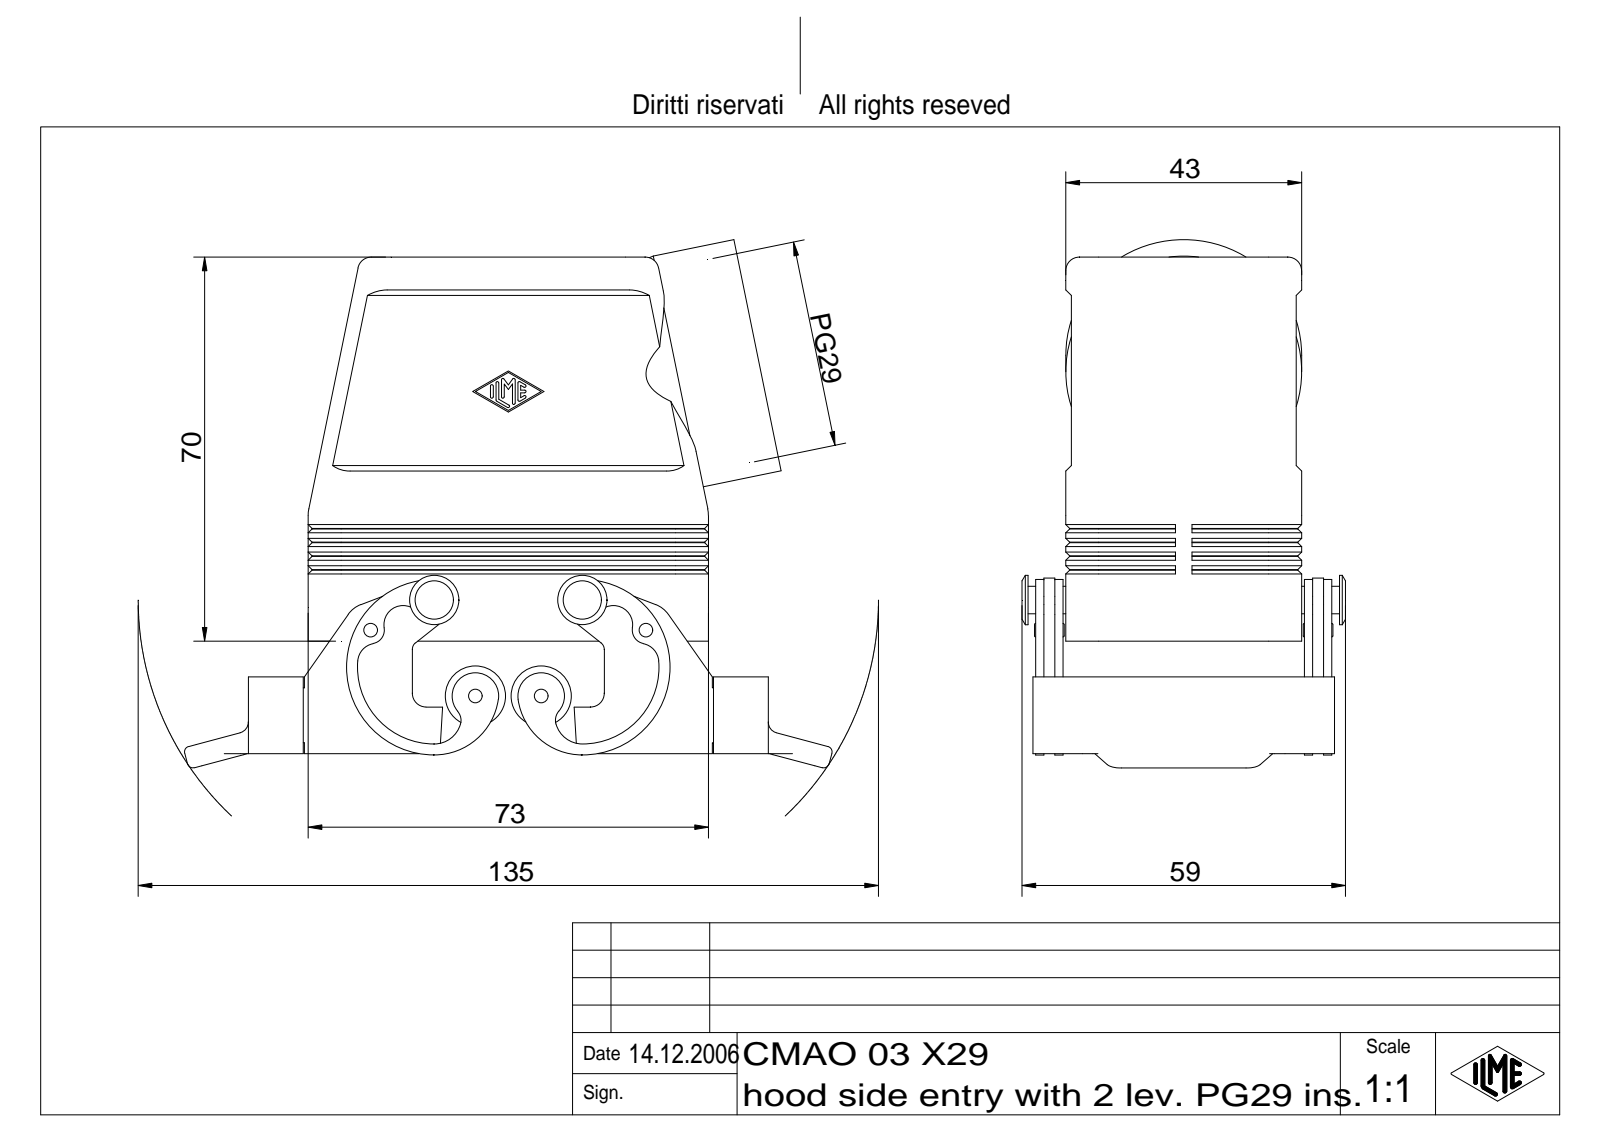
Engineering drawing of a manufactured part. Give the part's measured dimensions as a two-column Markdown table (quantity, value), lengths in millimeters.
| quantity | value |
| --- | --- |
| part name | CAO Tüllengehäuse 2 Bügel für einen Einsatz |
| STEP written by | Autodesk Inventor 7 (AUTOMOTIVE_DESIGN) |
| units | millimeters |
| bodies | 1 solid, 851 faces (245 planar, 231 cylindrical, 375 other) |
| overall size | 118.09 × 96.27 × 59 |
| volume | 76 522 mm³ |
| surface area | 52 282 mm² |
| round holes (diameter × count) | 2.5 × 2, 33.48 × 1, 35.48 × 1 |
| round bosses / shafts (diameter × count) | 11 × 2, 9 × 2, 5 × 2, 2 × 2, 43 × 1 |
| partial cylindrical surfaces (radius × count) | 0.25 × 14, 1 × 12, 2 × 10, 2.5 × 10, 6 × 10, 3 × 8, 3.5 × 4, 5 × 4 |
| main face-to-face distances | 2, 3, 42, 37, 39, 1, 40, 49, 5, 9 |
| hole center spacings | 50.2 |
